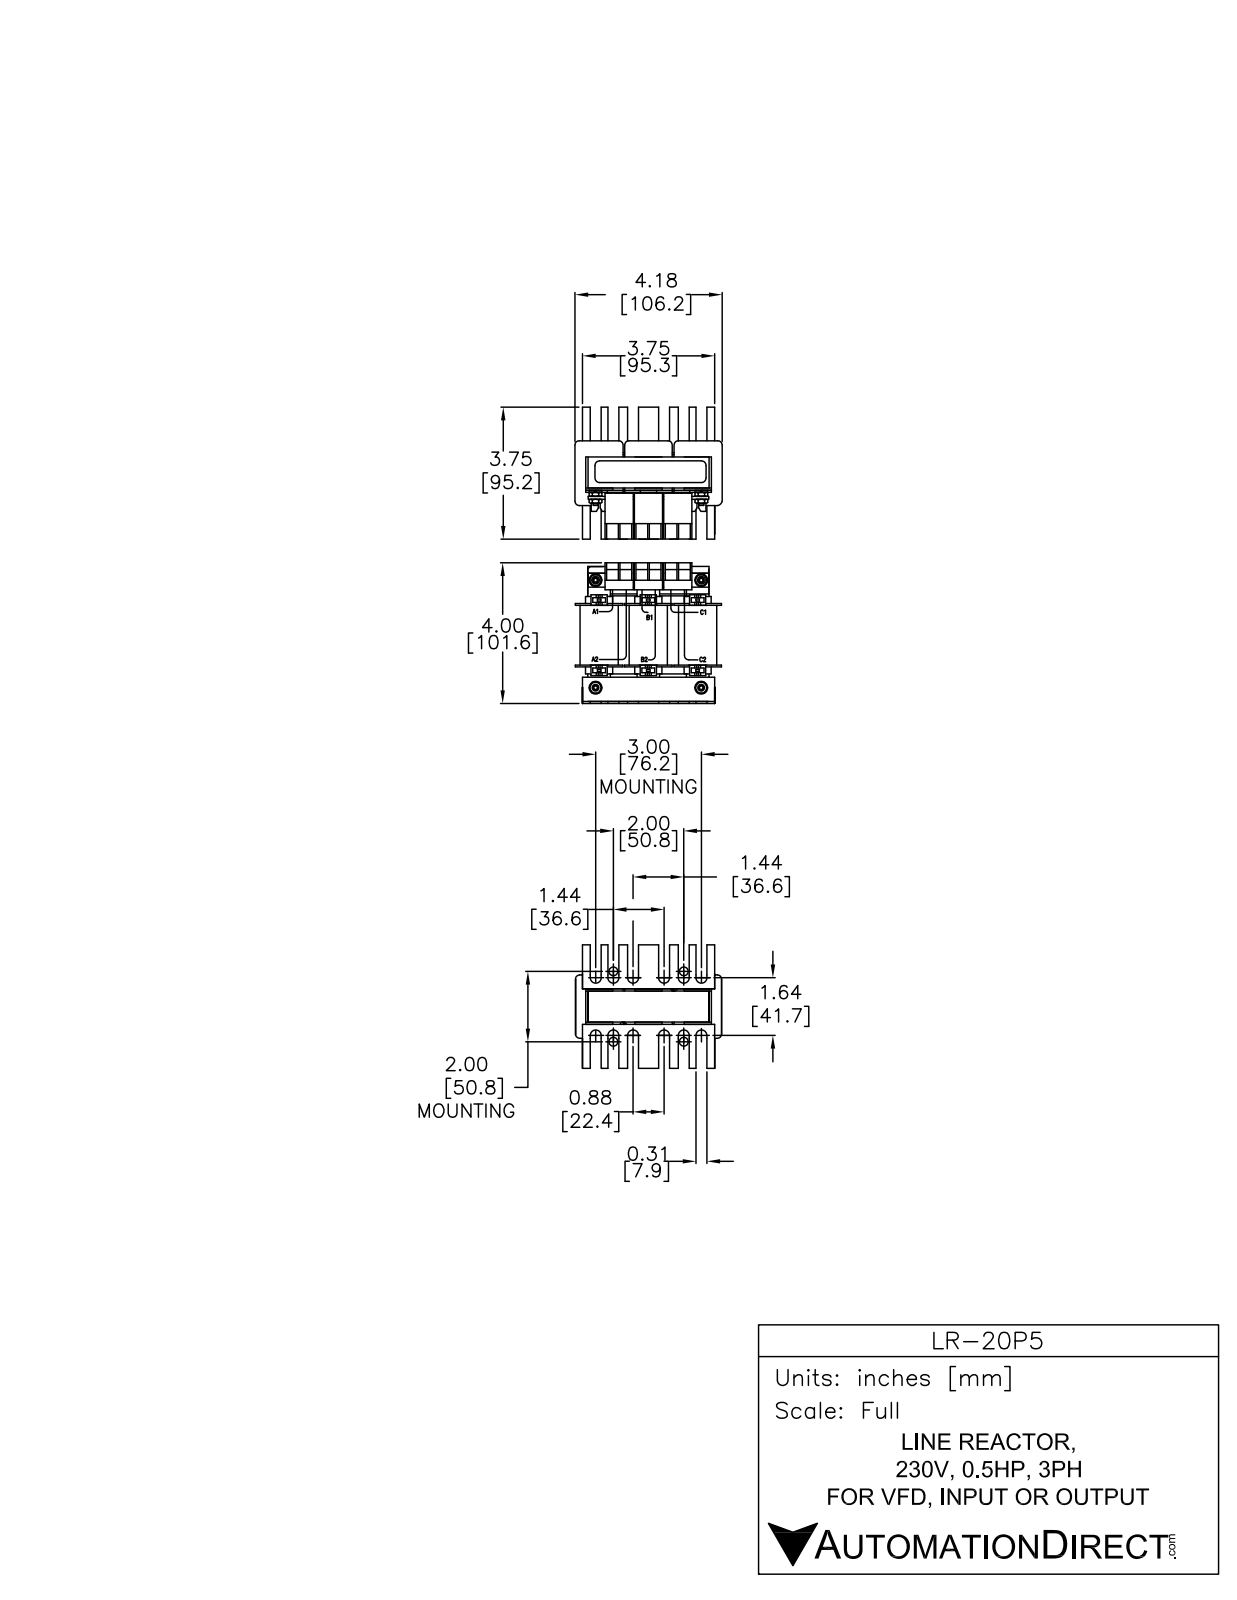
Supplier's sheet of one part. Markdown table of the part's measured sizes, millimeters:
| quantity | value |
| --- | --- |
| part name | LR-20P5 |
| STEP written by | SolidWorks 2011 (AUTOMOTIVE_DESIGN) |
| units | millimeters |
| bodies | 17 solids, 941 faces (743 planar, 198 cylindrical, 0 other) |
| overall size | 105.25 × 98.41 × 89.25 |
| volume | 272 326 mm³ |
| surface area | 99 223 mm² |
| round bosses / shafts (diameter × count) | 7.75 × 4, 3.5 × 4 |
| partial cylindrical surfaces (radius × count) | 4 × 50, 1.82 × 24, 8 × 12, 3 × 6, 0.86 × 3, 1.25 × 2 |
| main face-to-face distances | 5, 21.5, 2.75, 51, 26.25, 26.5, 7.5, 29, 71, 2.5 |
